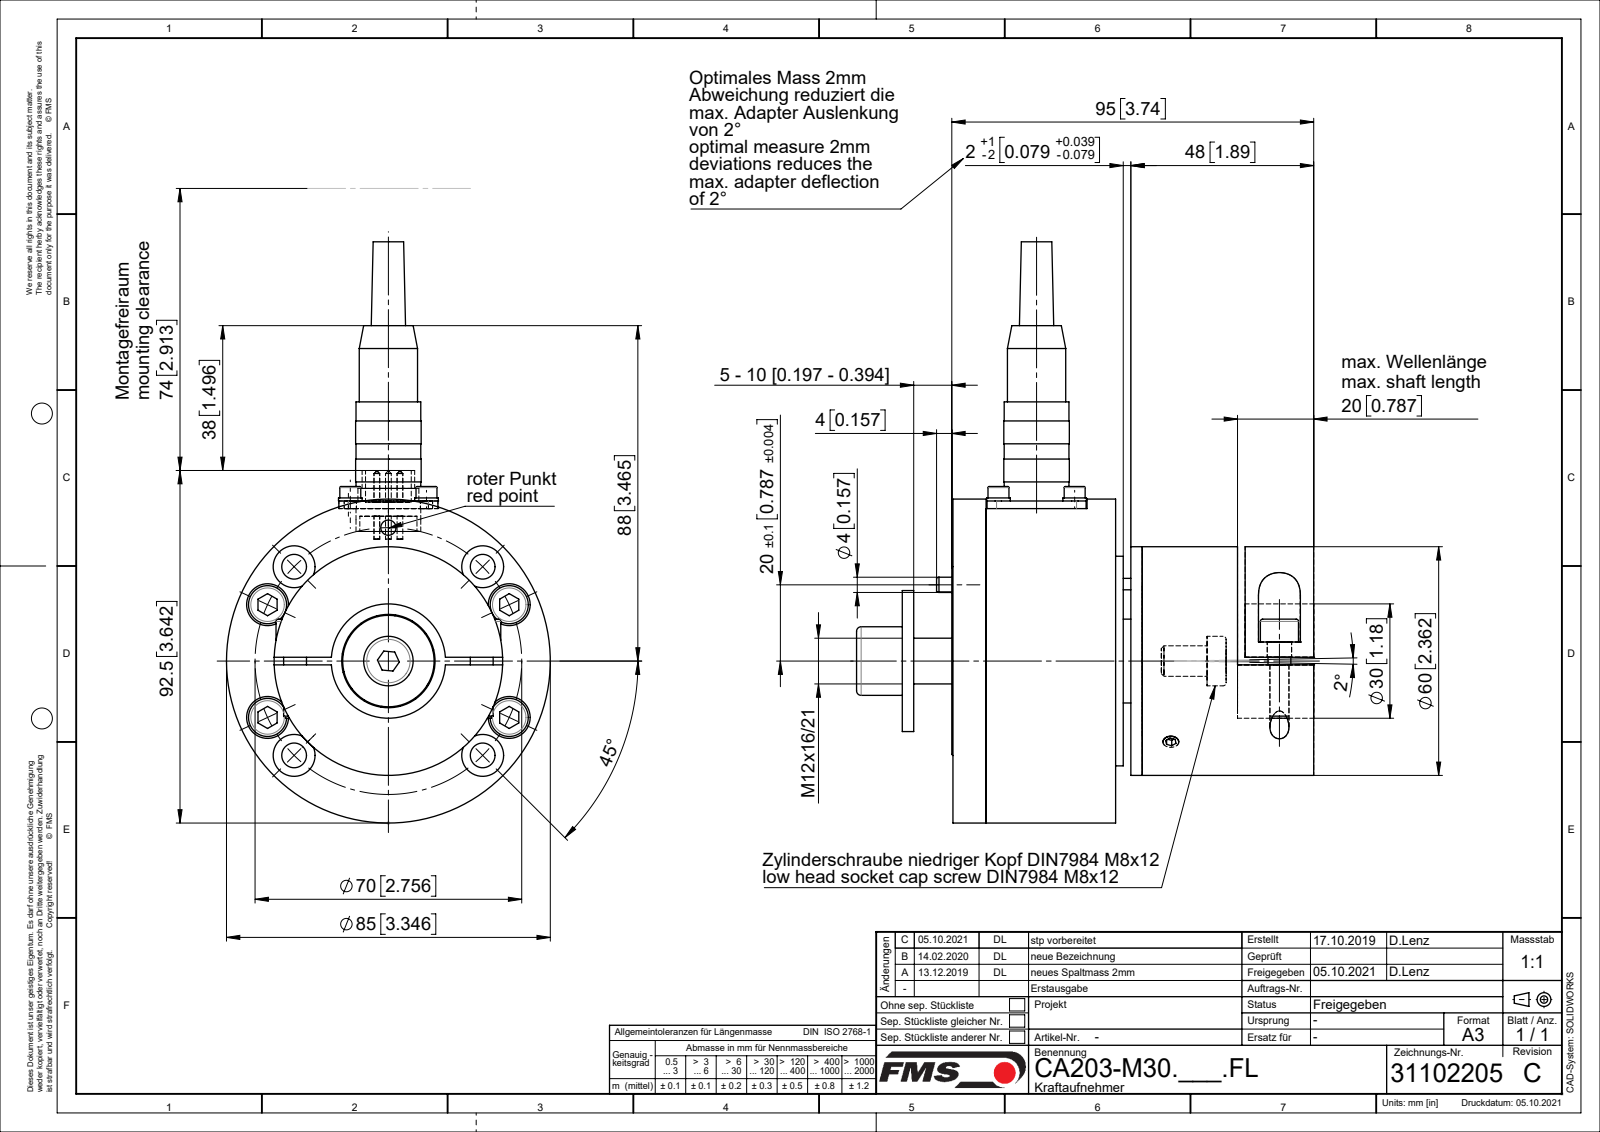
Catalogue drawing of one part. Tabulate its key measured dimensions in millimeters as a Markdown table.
| quantity | value |
| --- | --- |
| part name | 070910-4_01; Spannstift_ISO13337_D04x10; Kabeldose_M14x1_Mini_5pol; Sch DIN9021_M12 (+8 more) |
| STEP written by | SolidWorks 2018 (CONFIG_CONTROL_DESIGN) |
| units | millimeters |
| bodies | 43 solids, 785 faces (270 planar, 326 cylindrical, 189 other) |
| overall size | 152.5 × 120 × 85 |
| volume | 308 597 mm³ |
| surface area | 111 657 mm² |
| round holes (diameter × count) | 2.5 × 8, 6.5 × 8, 11 × 8, 5 × 6, 4 × 5, 3.1 × 4, 3.2 × 4, 3.6 × 4, 7 × 4, 3 × 2, 6.4 × 2, 4.2 × 1 |
| round bosses / shafts (diameter × count) | 3 × 8, 6 × 7, 10 × 6, 1.5 × 5, 6.2 × 4, 5.7 × 4, 5.5 × 4, 85 × 1 |
| partial cylindrical surfaces (radius × count) | 2.5 × 4, 5 × 2, 5.5 × 2 |
| main face-to-face distances | 2, 41, 45, 10, 30, 3, 50, 22, 60, 34 |
| hole center spacings | 35, 20, 24.78, 25.2, 32.8, 51.14, 56.46, 28.28 |
